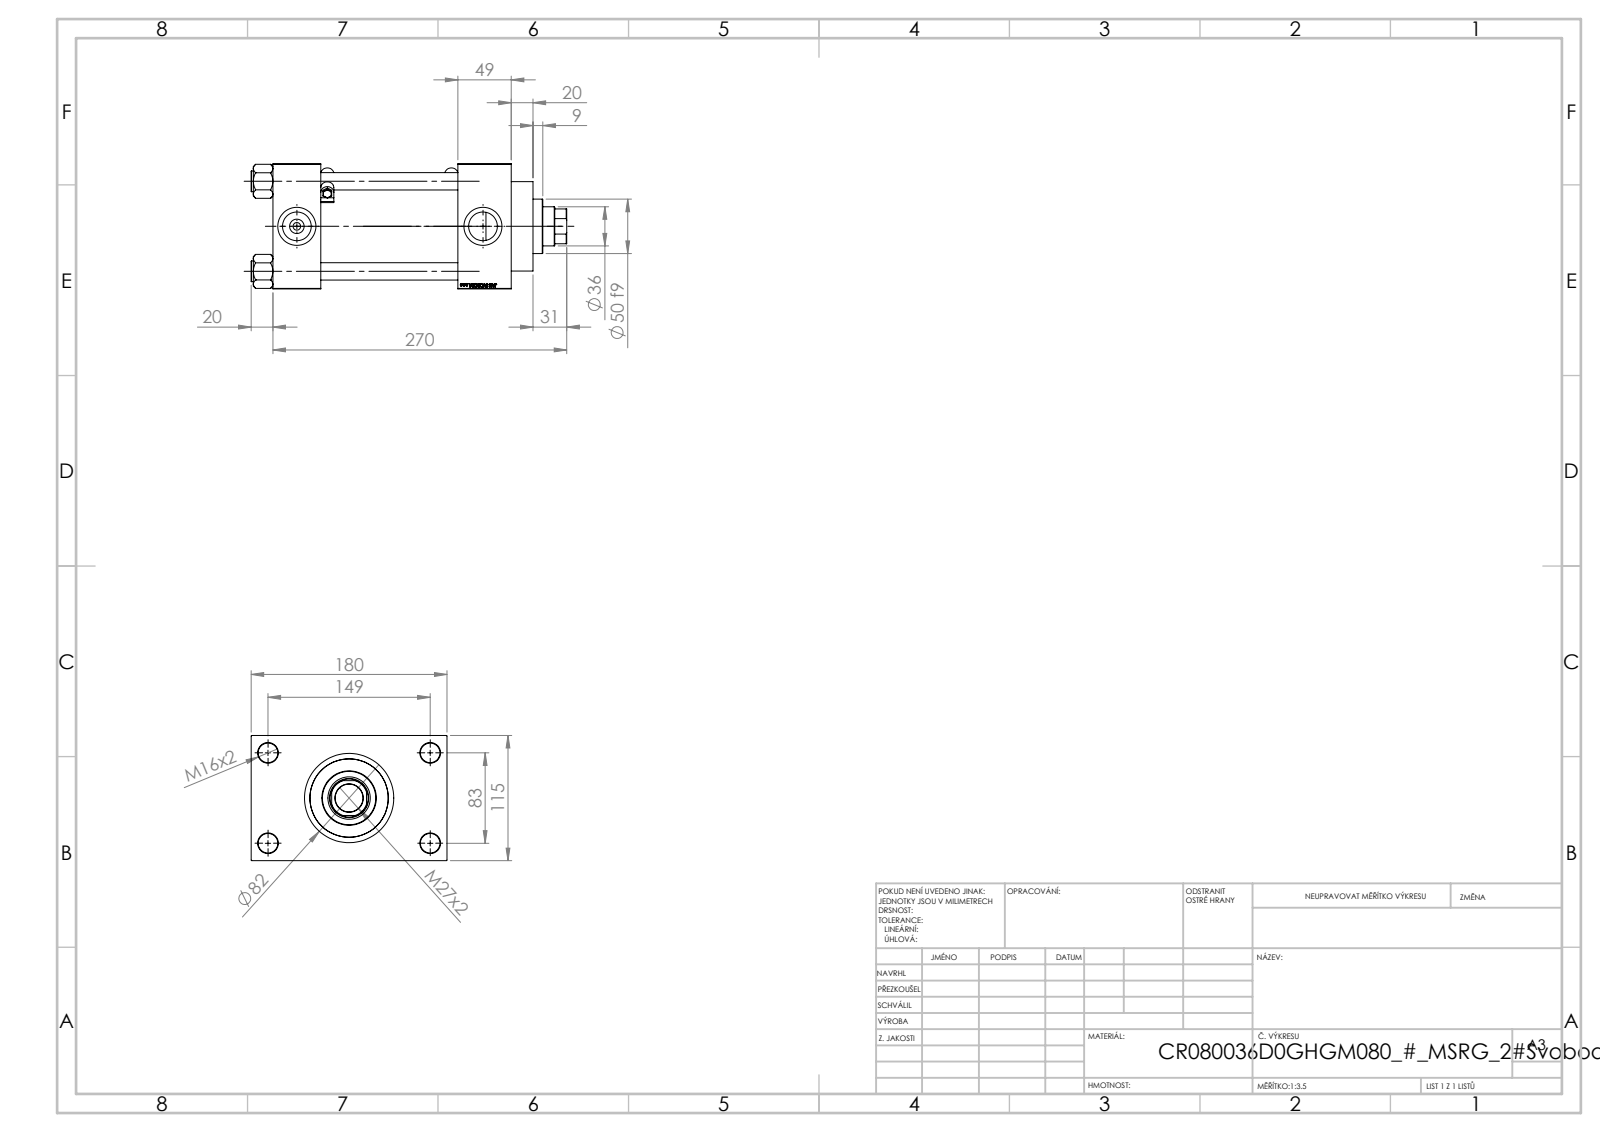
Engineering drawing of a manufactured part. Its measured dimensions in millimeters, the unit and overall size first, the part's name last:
Units: millimetres
Overall size (bounding box): 290 × 180 × 115
Round holes (diameter × count): ⌀16 ×4, ⌀18 ×4, ⌀7 ×2, ⌀26.44 ×2, ⌀35 ×2, ⌀25.5 ×1, ⌀36 ×1, ⌀39 ×1, ⌀61 ×1, ⌀72 ×1, ⌀80 ×1
Round bosses / shafts (diameter × count): ⌀19 ×4, ⌀5 ×2, ⌀2.5 ×2, ⌀86 ×1, ⌀82 ×1, ⌀50 ×1
Partial cylindrical surfaces — rounded edges, fillets, slot ends (radius × count): R0.5 ×12, R6 ×4, R17.5 ×1
Main face-to-face distances: 115, 126, 175, 49, 170, 44, 219, 32.5, 147.5, 180
Hole centre spacings: 33.15, 58.48, 82.7, 85.28, 89.24, 115.85, 142.43, 83
Volume: 2 143 000 mm³ · Surface area: 351 443 mm²
Bodies: 13 solids, 1215 faces (581 planar, 116 cylindrical, 518 other)
Part name (STEP PRODUCT): V215CR_D_Body; V215CR_VCP_D; MSRF_MSRG1; V215_VC_A (+2 more)
STEP written by: SolidWorks 2019 (CONFIG_CONTROL_DESIGN)
